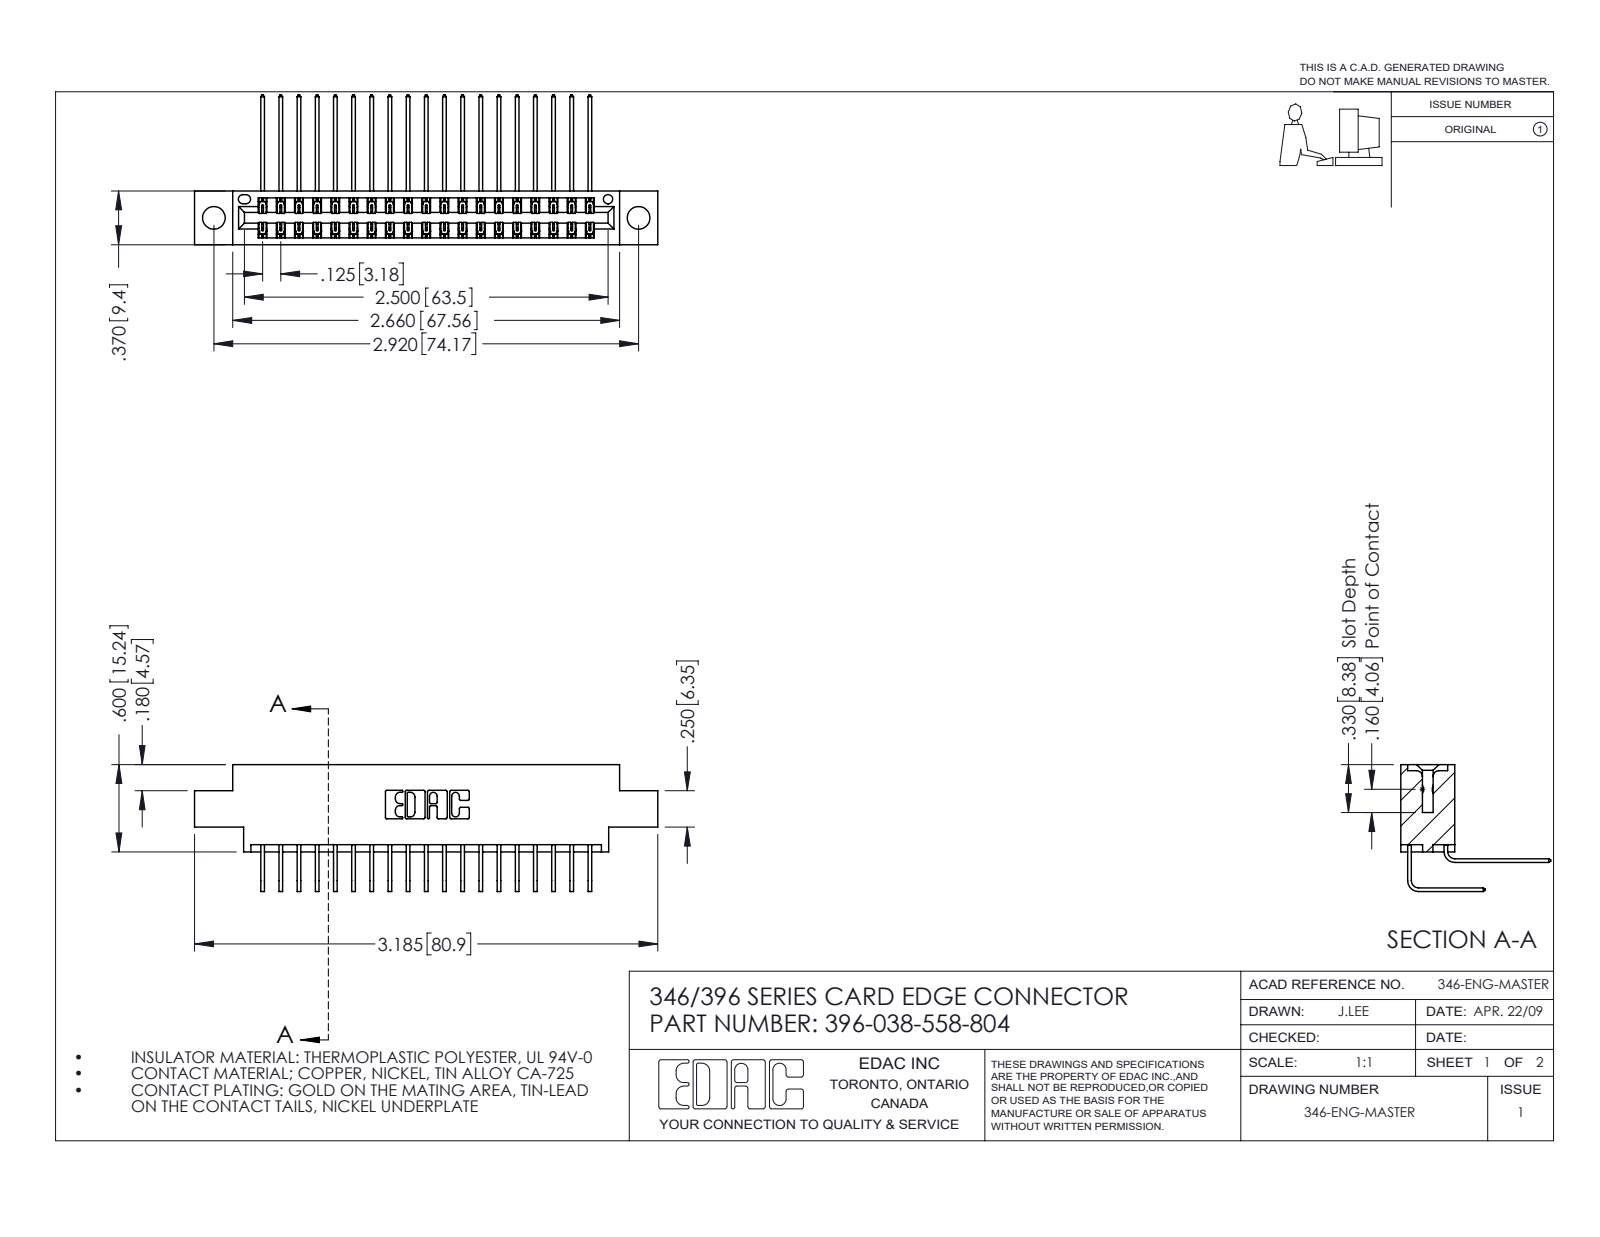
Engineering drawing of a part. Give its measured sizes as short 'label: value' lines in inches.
name: 346 Part_0.170 Offset - 0.156 Dia-TH; 396-038-558-804; 345-292-001_558 Tail - 2; 345-292-001_558 559 Tail - 1
written by: SolidWorks 2016 (CONFIG_CONTROL_DESIGN)
unit: in
bodies: 39 solids, 2178 faces (1486 planar, 692 cylindrical, 0 other)
size: 3.185 × 1.03 × 0.873
volume: 0.469 in³; area: 17.44 in²
holes: 2× ⌀0.156, 1× ⌀0.064
rounds: 57× R0.006, 22× R0.01, 6× R0.007, 6× R0.031, 3× R0.026, 2× R0.014, 2× R0.022, 2× R0.024
face distances: 0.322, 0.048, 0.37, 0.25, 0.025, 0.298, 0.072, 0.275, 0.148, 0.222
hole spacings: 0.246, 2.713, 2.92
